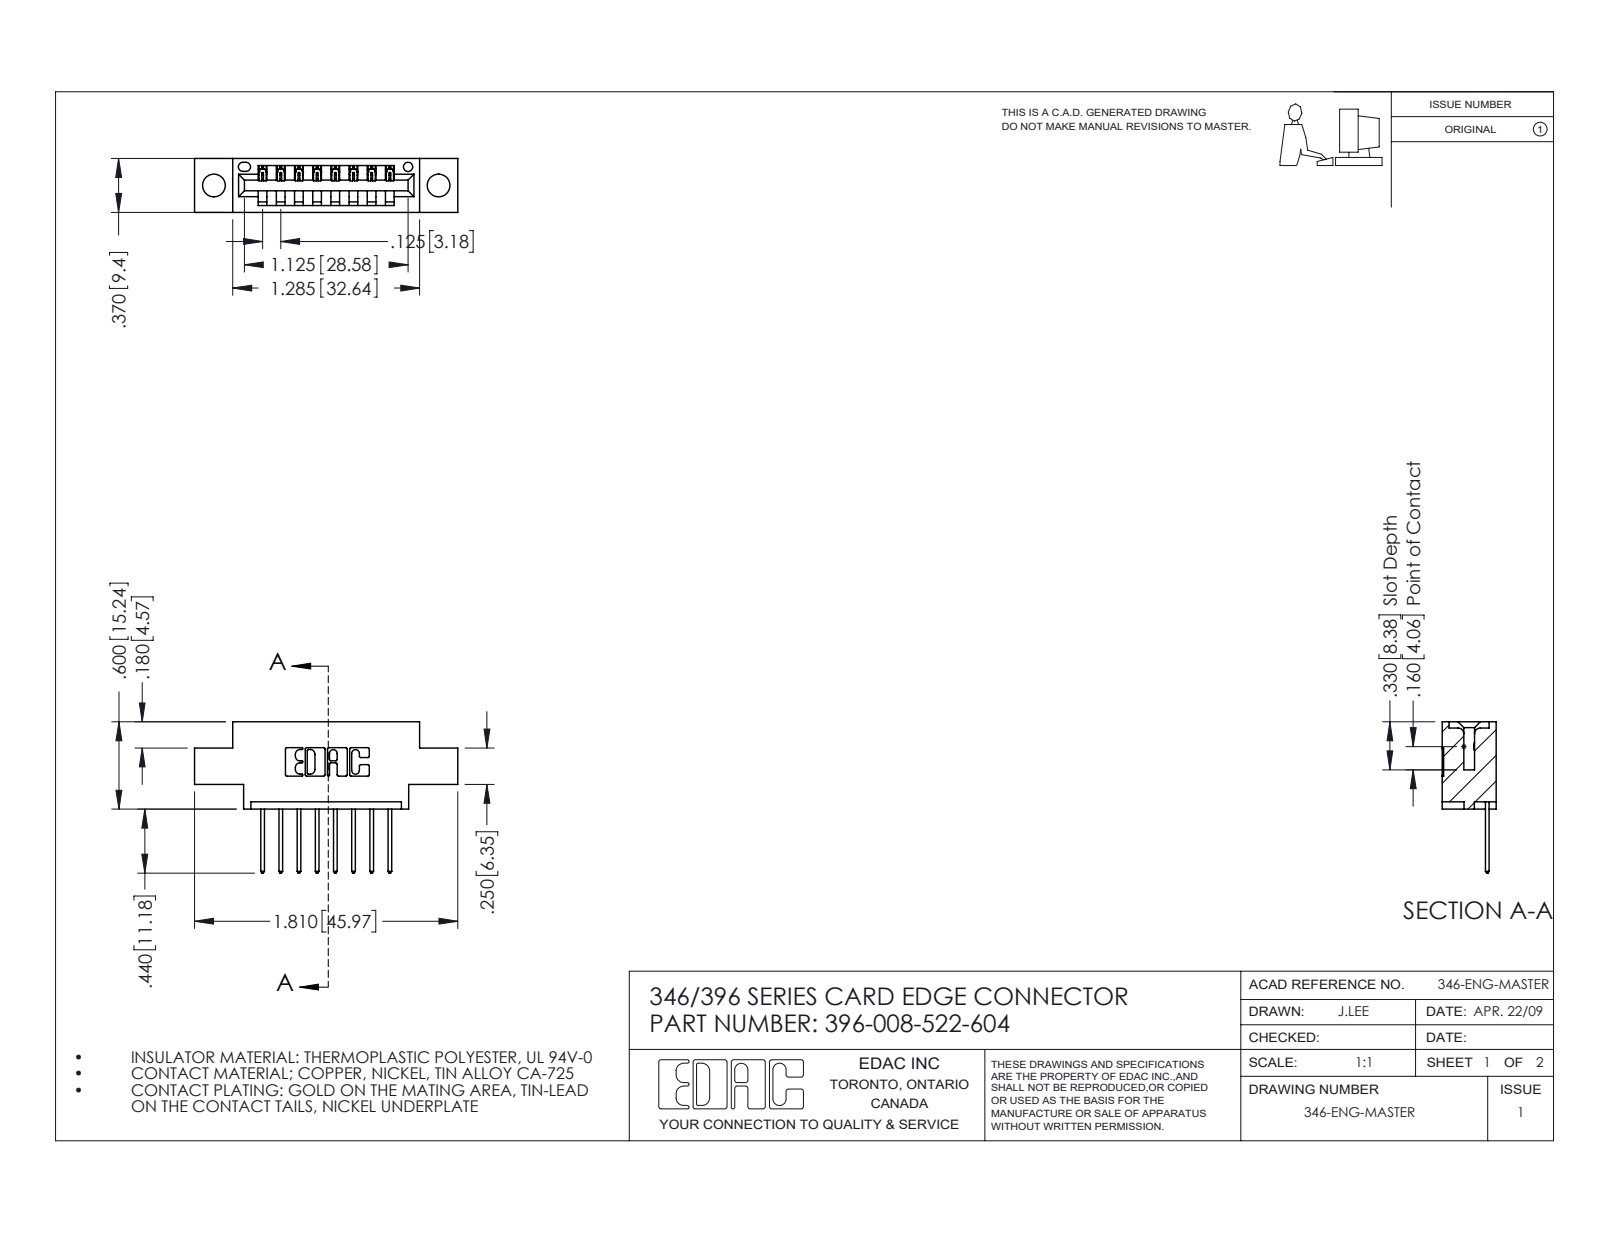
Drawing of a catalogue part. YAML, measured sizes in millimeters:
part_name: "345-292-001_345-293-122; 346 Part_0.170 Offset - 0.156 Dia-TH; 396-008-522-604"
step_written_by: "SolidWorks 2016 (CONFIG_CONTROL_DESIGN)"
units: millimeters
bodies: {solids: 9, faces: 590, planar: 400, cylindrical: 190, other: 0}
overall_size: [46, 26.4, 9.4]
volume: 3930
surface_area: 4534
round_holes:
  - {diameter: 4, count: 2}
  - {diameter: 1.6, count: 1}
partial_cylinders:
  - {radius: 0.3, count: 22}
  - {radius: 0.2, count: 16}
  - {radius: 0.3, count: 16}
  - {radius: 0.2, count: 6}
  - {radius: 0.8, count: 6}
  - {radius: 0.7, count: 3}
  - {radius: 0.8, count: 2}
  - {radius: 1, count: 2}
face_to_face_distances: [6.4, 9.4, 1.2, 8.2, 1.8, 7.6, 0.6, 3.8, 5.6, 2.5]
hole_center_spacings: [6.2, 34.1, 39.2]
